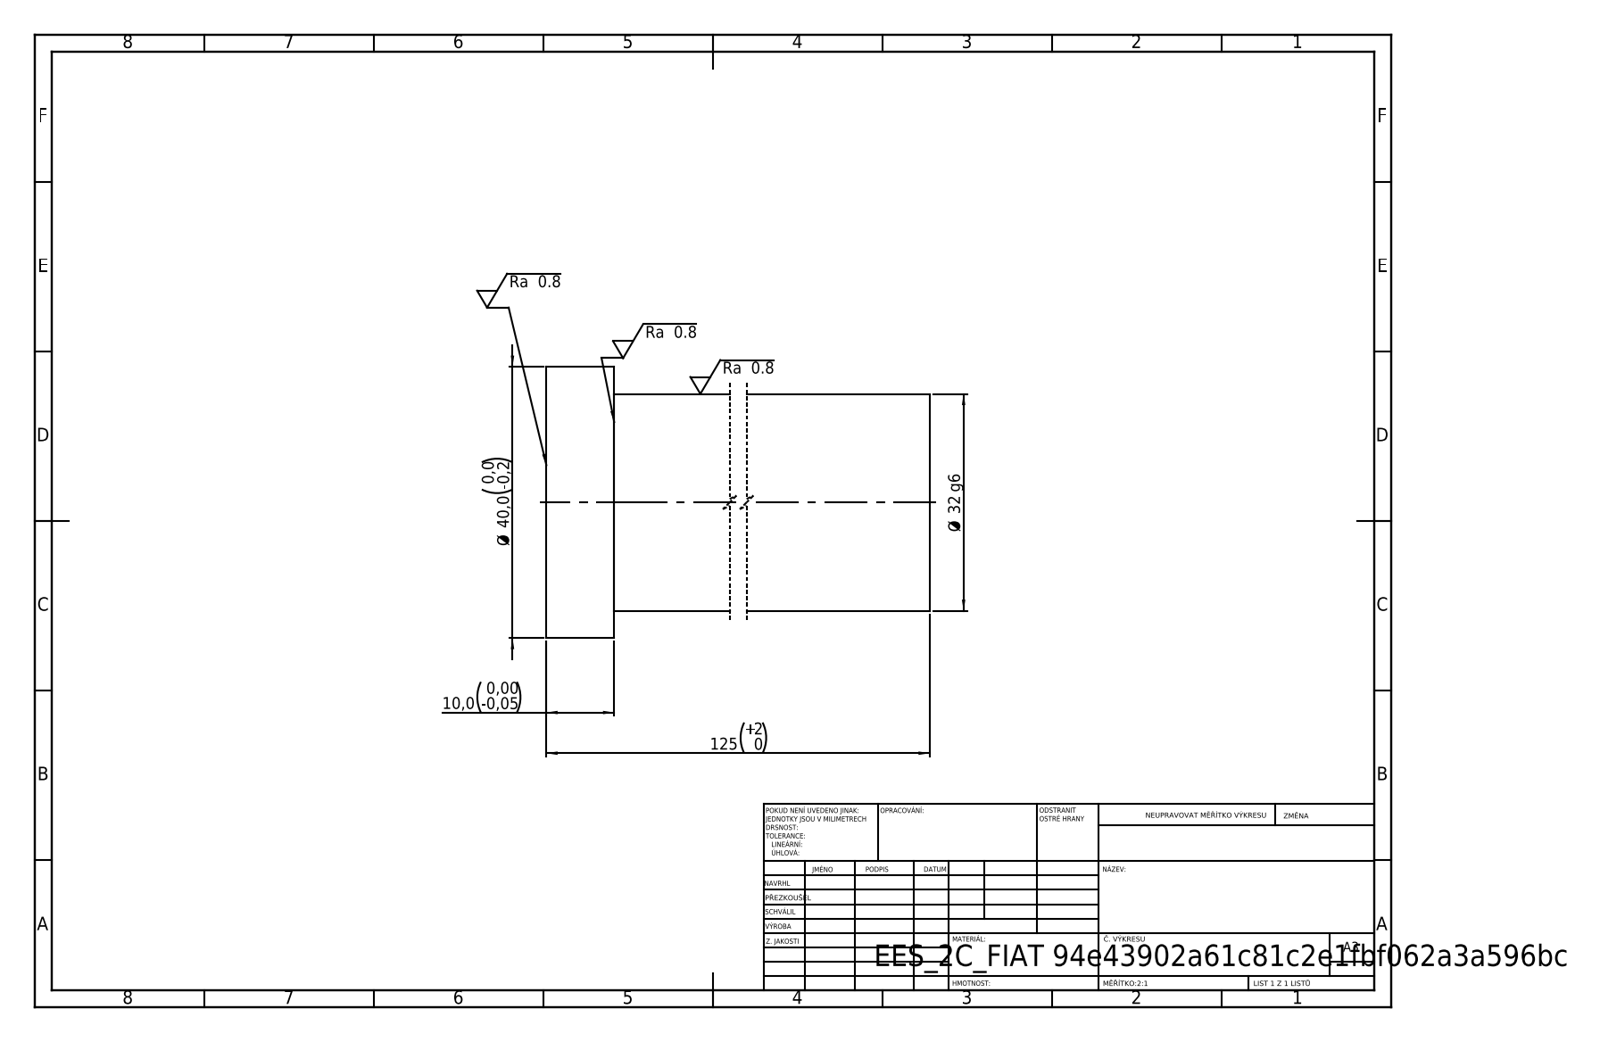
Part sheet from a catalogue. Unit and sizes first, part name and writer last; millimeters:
Units: millimetres
Overall size (bounding box): 125 × 40 × 40
Round bosses / shafts (diameter × count): ⌀40 ×1, ⌀32 ×1
Main face-to-face distances: 125, 10, 115
Volume: 105 055 mm³ · Surface area: 15 331 mm²
Bodies: 1 solid, 7 faces (3 planar, 4 cylindrical, 0 other)
STEP written by: SolidWorks 2019 (CONFIG_CONTROL_DESIGN)
